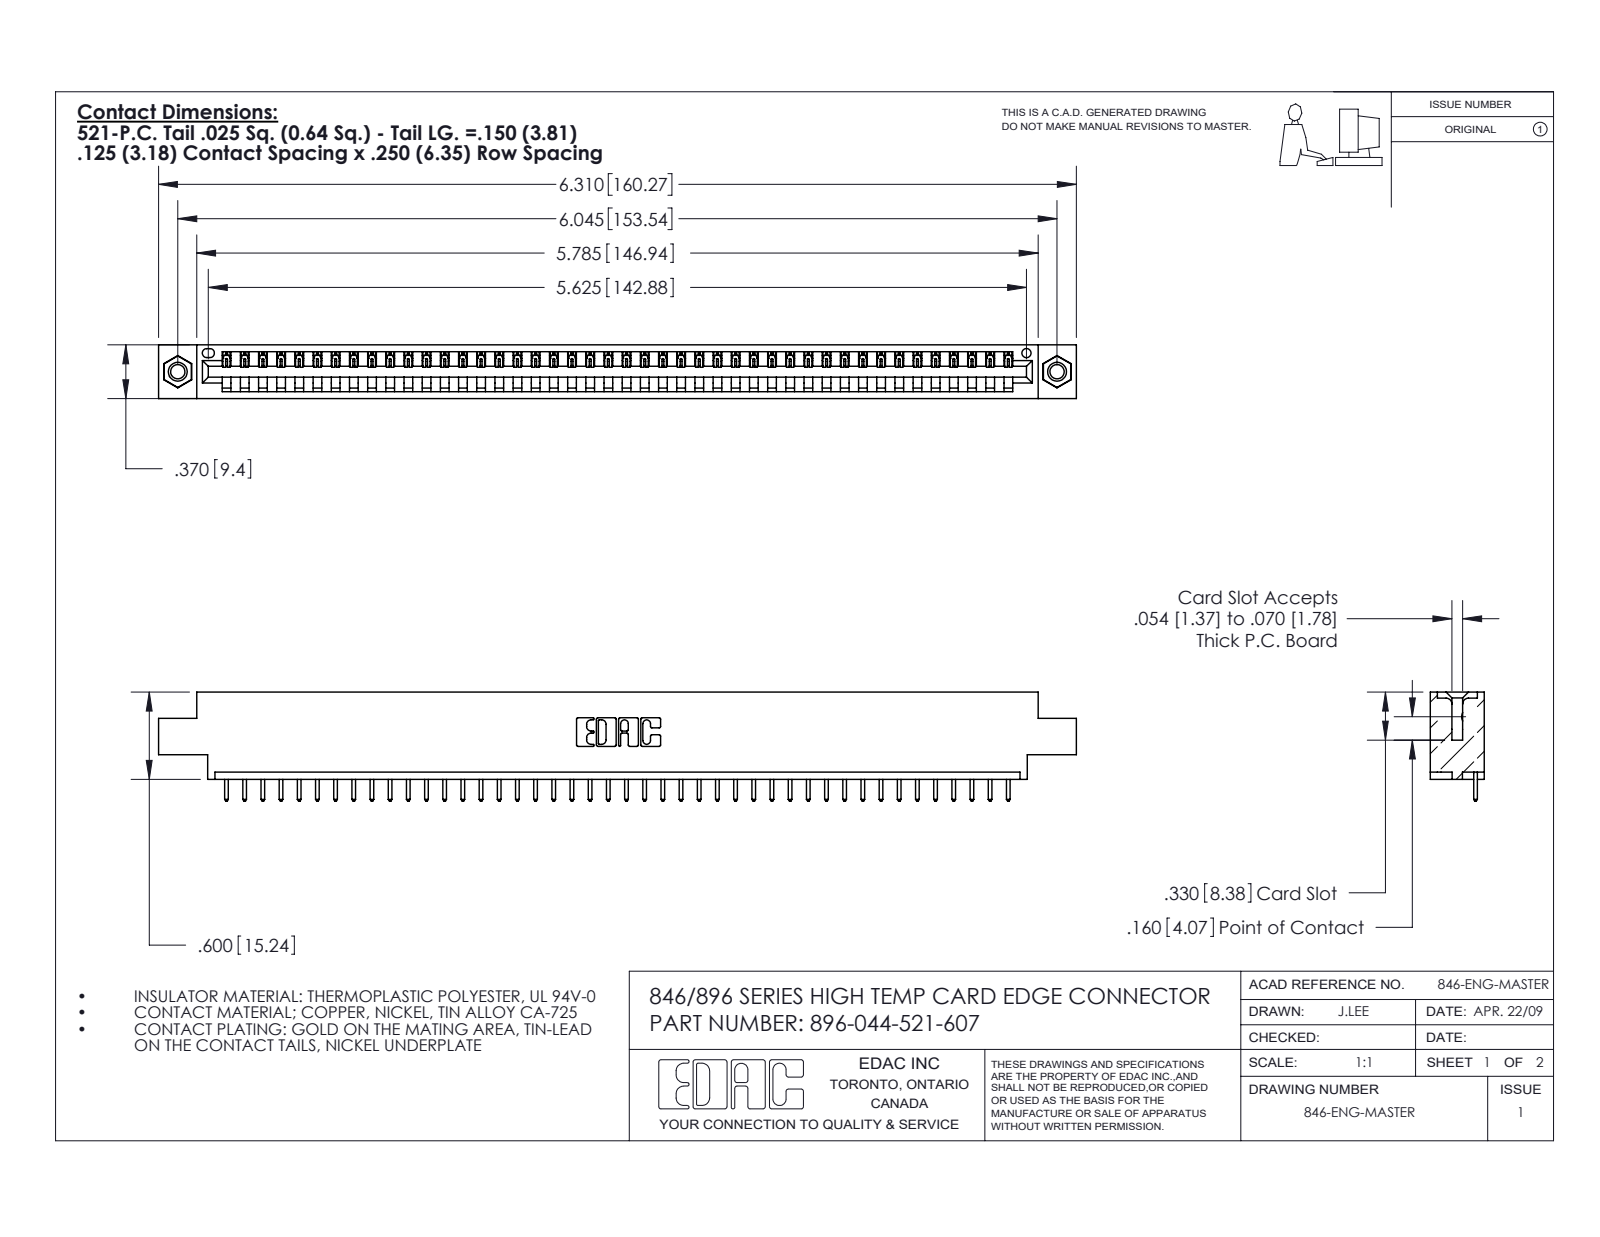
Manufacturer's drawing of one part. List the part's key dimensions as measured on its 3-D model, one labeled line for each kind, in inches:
Part name (STEP PRODUCT): 346 Part_0.170 Offset - 0.156 Dia-TI; 345-250-001_345-250-005-103; 345-292-001_345-293-121; 396-044-521-607
STEP written by: SolidWorks 2016 (CONFIG_CONTROL_DESIGN)
Units: inches
Bodies: 47 solids, 2738 faces (1872 planar, 850 cylindrical, 16 other)
Overall size (bounding box): 6.31 × 0.75 × 0.37
Volume: 0.919 in³ · Surface area: 28.74 in²
Round holes (diameter × count): ⌀0.098 ×2, ⌀0.125 ×2, ⌀0.156 ×2, ⌀0.064 ×1
Round bosses / shafts (diameter × count): ⌀0.155 ×2
Partial cylindrical surfaces — rounded edges, fillets, slot ends (radius × count): R0.006 ×88, R0.01 ×88, R0.01 ×22, R0.007 ×6, R0.031 ×6, R0.026 ×3, R0.031 ×2, R0.04 ×2
Main face-to-face distances: 0.048, 0.322, 0.37, 0.25, 0.072, 0.298, 0.025, 0.222, 0.148, 0.1
Hole centre spacings: 0.246, 5.836, 6.045
